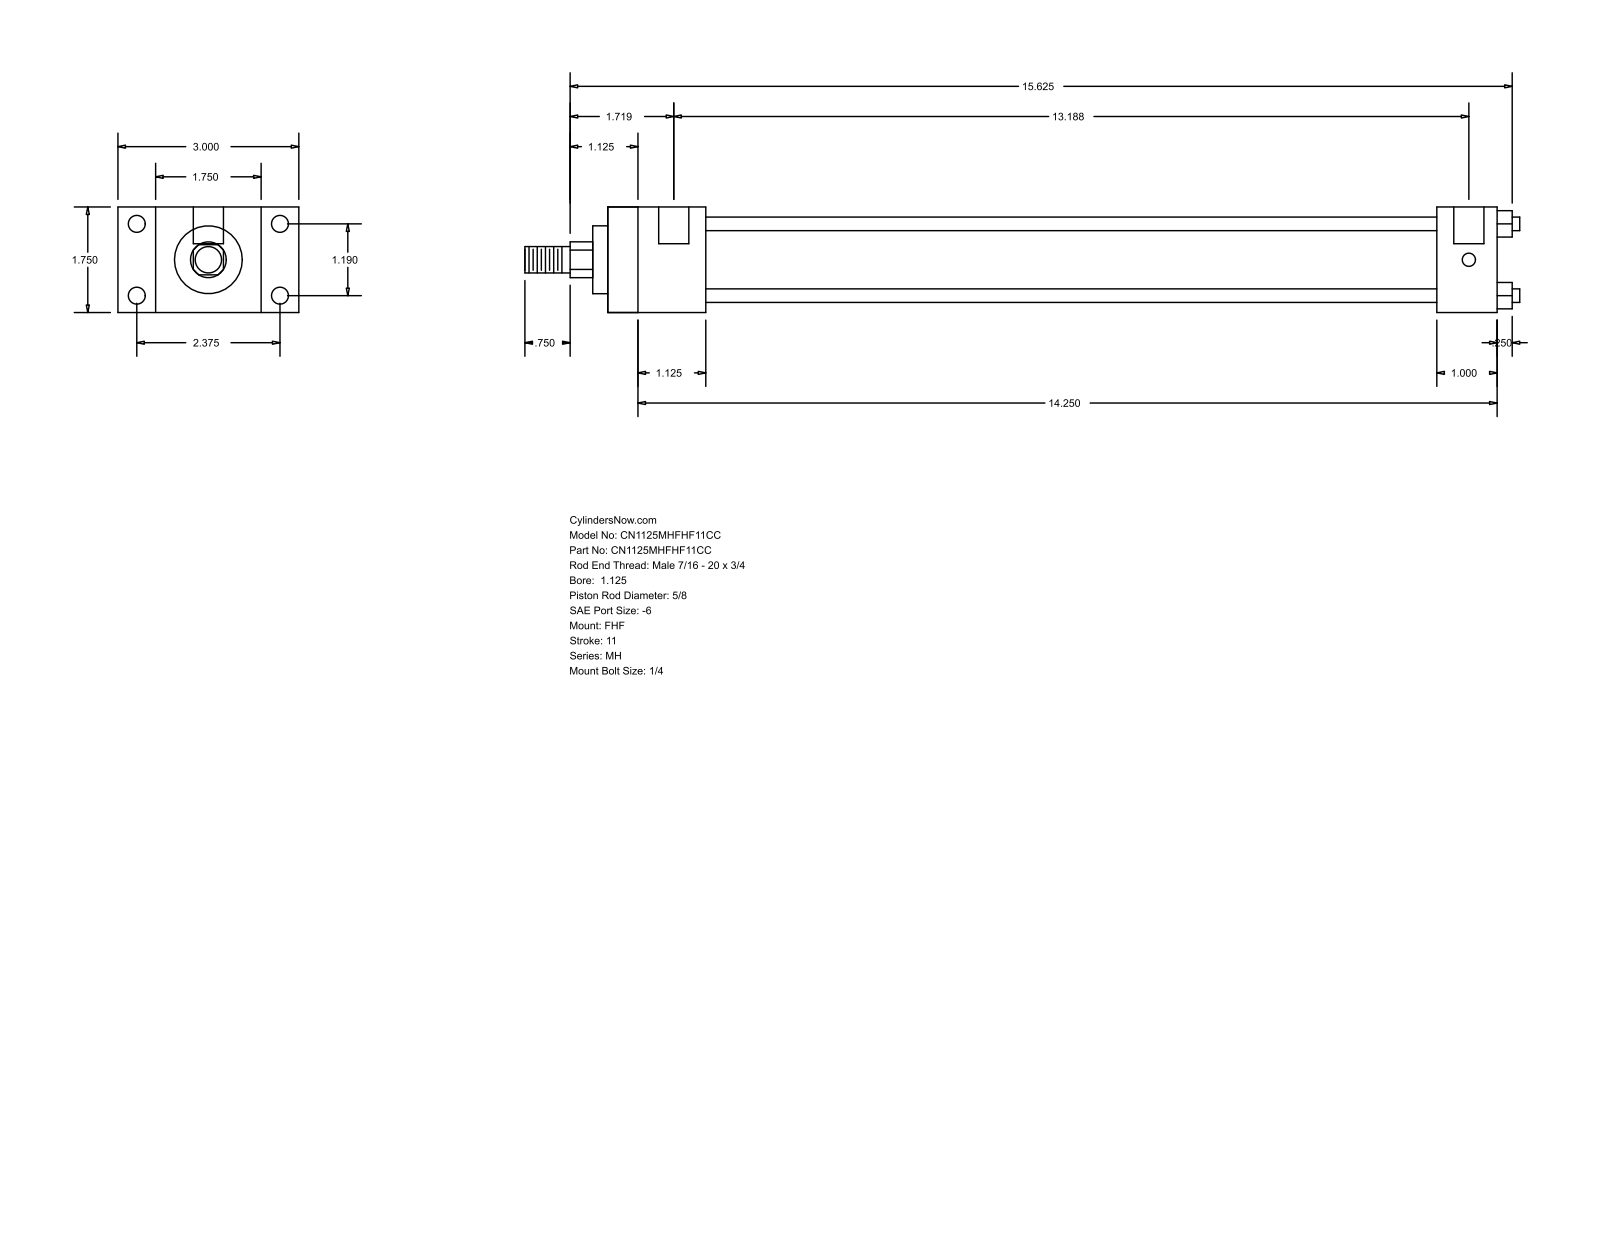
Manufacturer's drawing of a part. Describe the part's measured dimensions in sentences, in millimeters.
The part is named "MH_FHF__0112_0.625". Its 3-D file was written by "GSSL Pune (CONFIG_CONTROL_DESIGN)". It is 0 solids with 88 faces: 60 planar, 28 cylindrical and 0 other. Overall it measures 419.1 by 76.2 by 44.45 millimeters. Round holes: 4 of diameter 5.56, 4 of diameter 7.14, 2 of diameter 12.7. Round bosses or shafts: 4 of diameter 5.71, 1 of diameter 34.92, 1 of diameter 28.57, 1 of diameter 15.88, 1 of diameter 11.11. Partial cylindrical surfaces (rounded edges, fillets, slot ends): 1 of radius 7.54. The main face-to-face distances are 44.46, 15.87, 60.33, 41.27, 76.2, 374.64, 333.37, 25.4, 349.24, 307.97. The hole center spacings are 30.22, 60.32, 67.47, 331.79, 3.17, 334.96.
